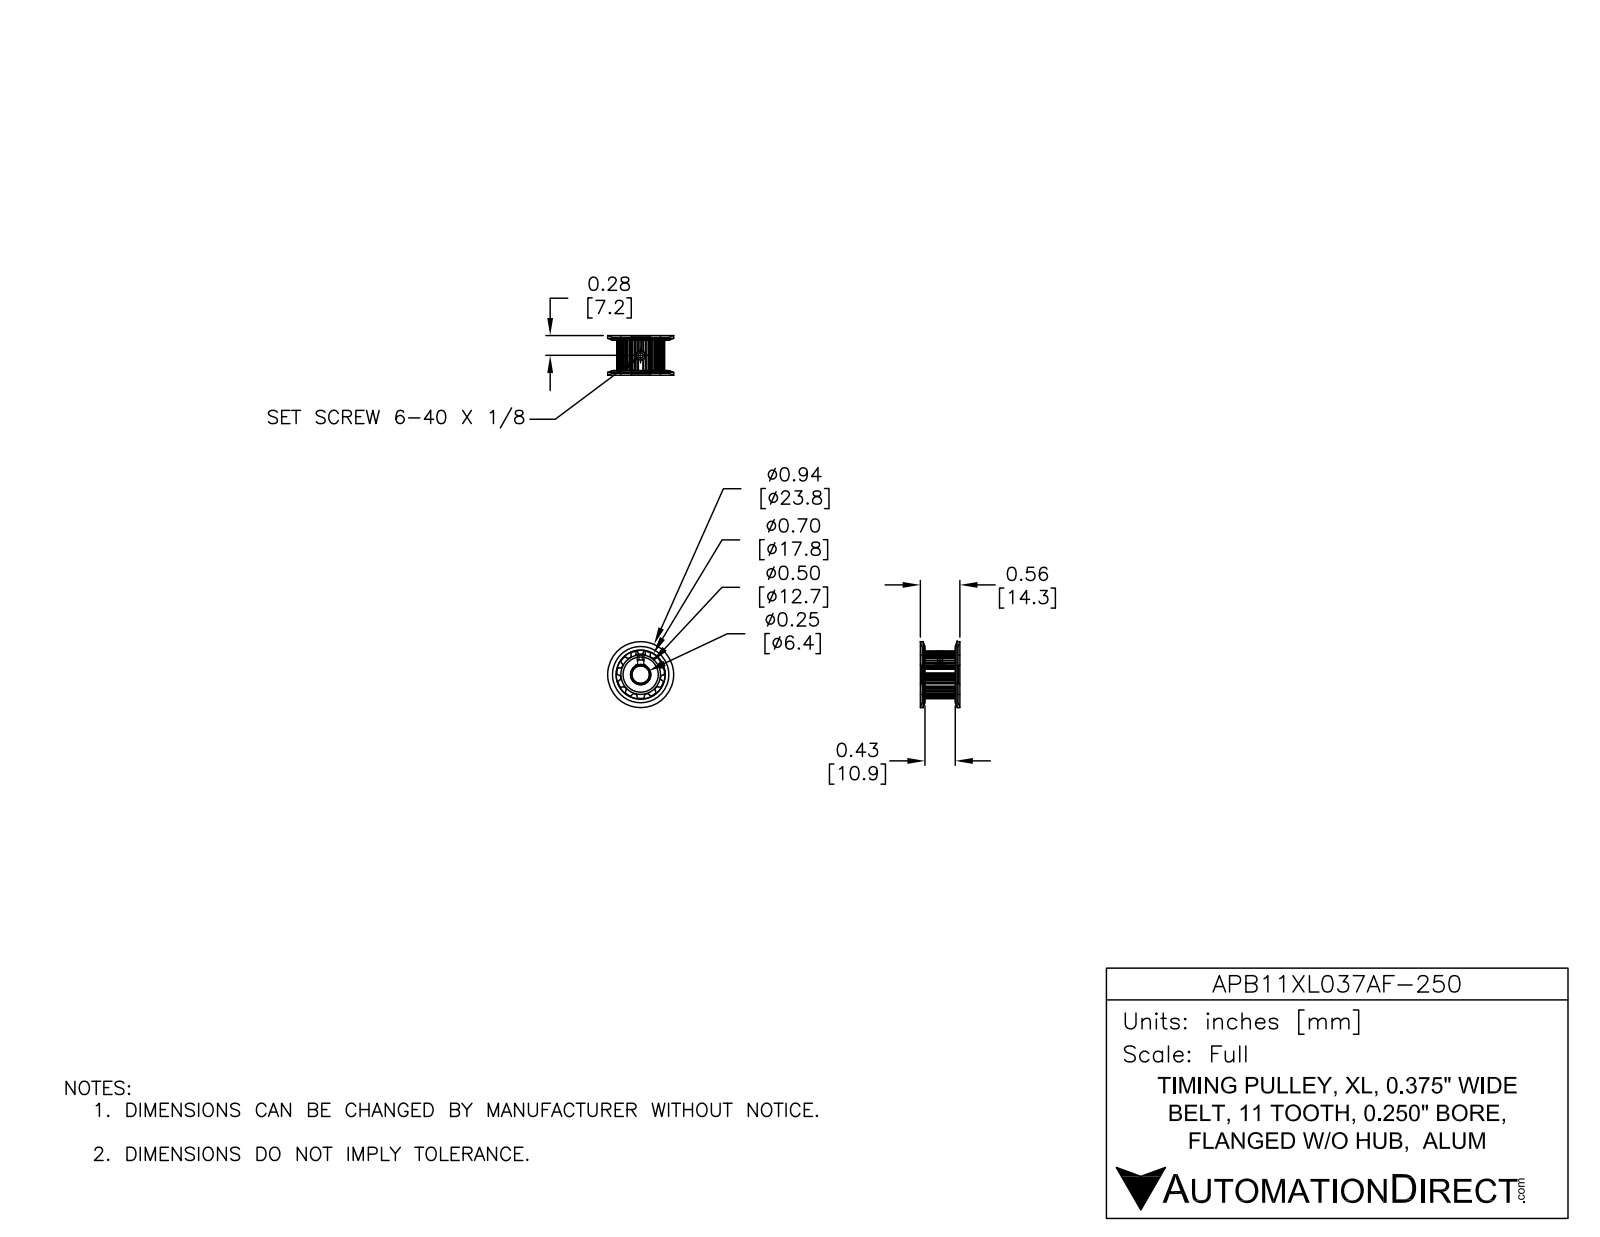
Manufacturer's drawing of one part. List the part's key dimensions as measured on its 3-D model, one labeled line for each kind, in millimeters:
Part name (STEP PRODUCT): APB11XL037AF-250
STEP written by: SolidWorks 2014 (AUTOMOTIVE_DESIGN)
Units: millimetres
Bodies: 1 solid, 145 faces (46 planar, 78 cylindrical, 21 other)
Overall size (bounding box): 23.8 × 23.8 × 14.3
Volume: 2 700 mm³ · Surface area: 2 588 mm²
Round holes (diameter × count): ⌀2.2 ×2, ⌀6.4 ×1
Round bosses / shafts (diameter × count): ⌀12.6 ×1
Partial cylindrical surfaces — rounded edges, fillets, slot ends (radius × count): R0.4 ×42, R1.6 ×1, R1.6 ×1, R7.2 ×1
Main face-to-face distances: 0.8, 12.7, 13.5, 14.3, 1.6, 11.9, 11.1, 17.3
